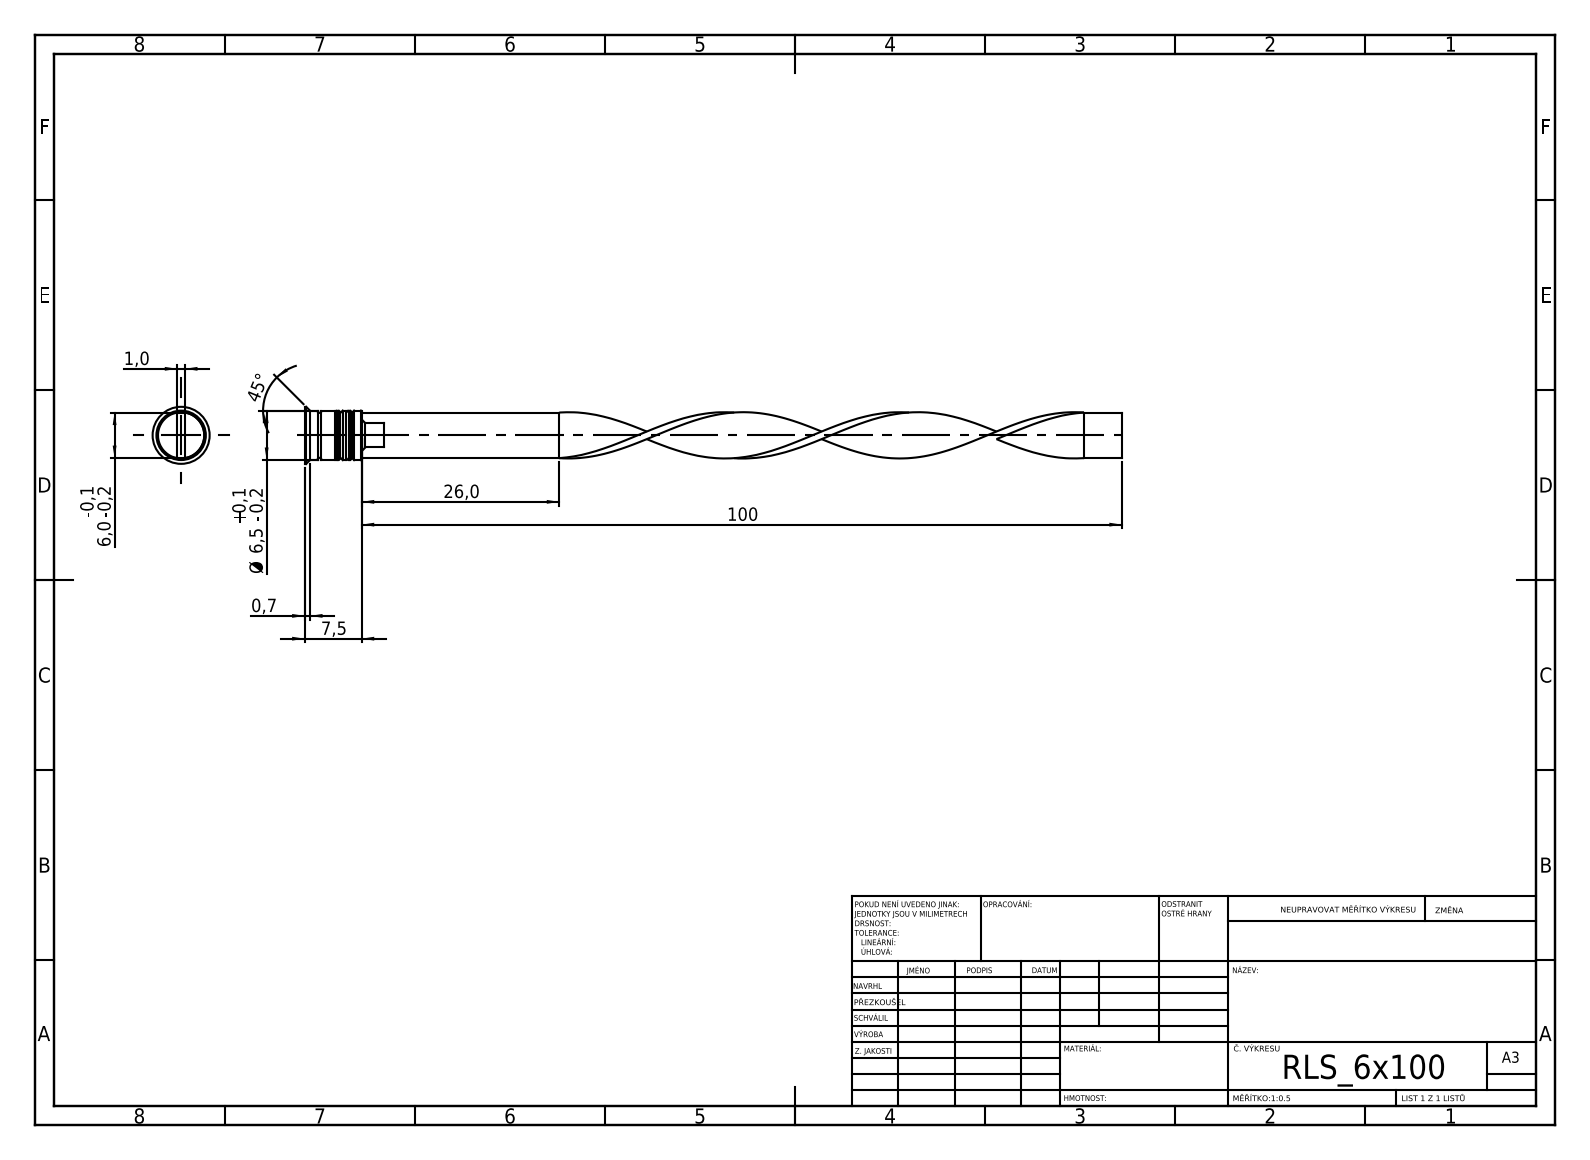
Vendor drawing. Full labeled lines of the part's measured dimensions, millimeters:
STEP written by: SolidWorks 2019 (CONFIG_CONTROL_DESIGN)
Units: millimetres
Bodies: 3 solids, 88 faces (36 planar, 23 cylindrical, 29 other)
Overall size (bounding box): 107.5 × 7.5 × 7.5
Volume: 890 mm³ · Surface area: 1 867 mm²
Round bosses / shafts (diameter × count): ⌀7.5 ×1, ⌀6.5 ×1, ⌀5.9 ×1, ⌀3.5 ×1, ⌀3.3 ×1
Main face-to-face distances: 1, 1.5, 0.7, 6, 4, 2.2, 5.5, 6.2, 0.8, 4.7
